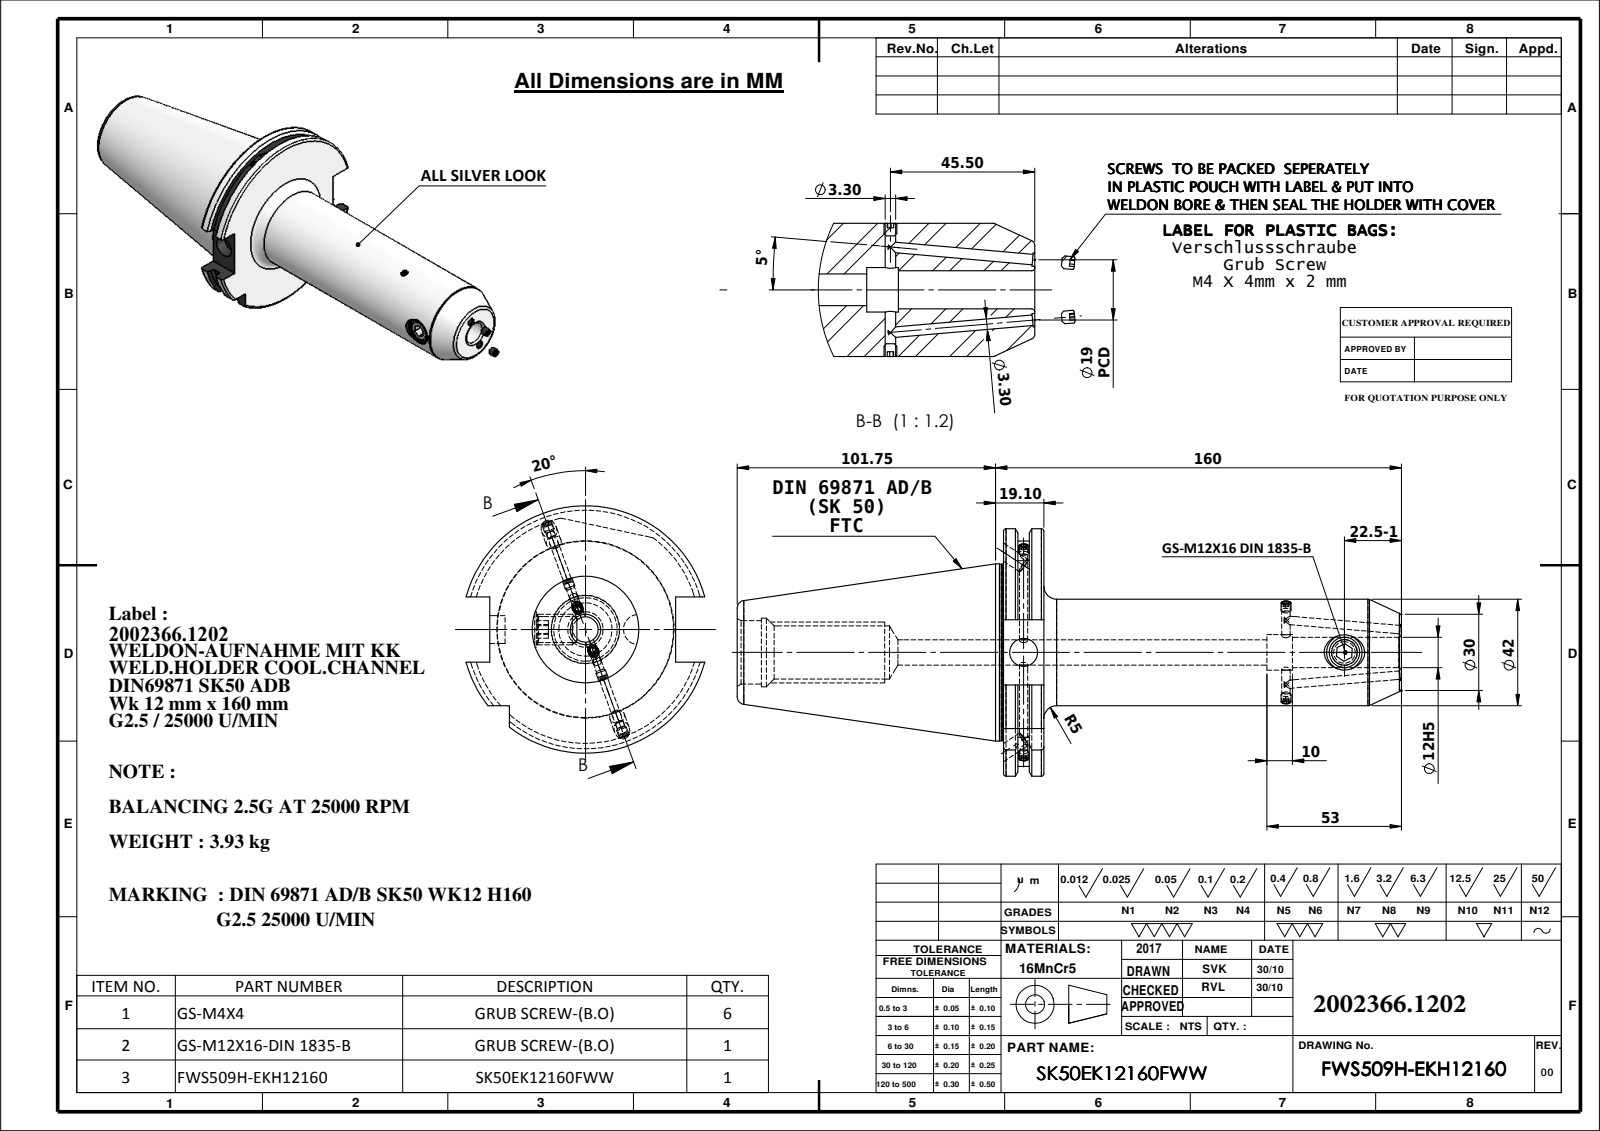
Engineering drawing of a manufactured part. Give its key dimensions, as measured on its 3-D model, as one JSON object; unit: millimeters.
{"part_name": "M12X16_ISO 4026 - M12 x 12-N; Copy of M4X4_DIN 913 - M4 x 4-N; M4X4_DIN 913 - M4 x 4-N; 91506-WK212160 (+1 more)", "step_written_by": "SolidWorks 2009 (CONFIG_CONTROL_DESIGN)", "units": "millimeters", "bodies": {"solids": 8, "faces": 252, "planar": 95, "cylindrical": 81, "other": 76}, "overall_size": [274.44, 97.5, 94.05], "volume_mm3": 510566, "surface_area_mm2": 68628, "round_holes": [[3.3, 4], [4.2, 2], [6, 2], [14, 2], [10, 1], [10.2, 1], [11, 1], [12, 1], [21, 1], [25, 1], [27, 1]], "round_bosses_or_shafts": [[4, 6], [69.85, 1], [69.45, 1], [42, 1], [12, 1]], "partial_cylinders_radius": [[44.9, 1], [48.75, 1]], "face_to_face_distances": [15.9, 10.15, 5.75, 5.66, 4.49, 10.24, 156.8, 151.14, 146.65, 140.9], "hole_center_spacings": [103.4, 126.4]}
